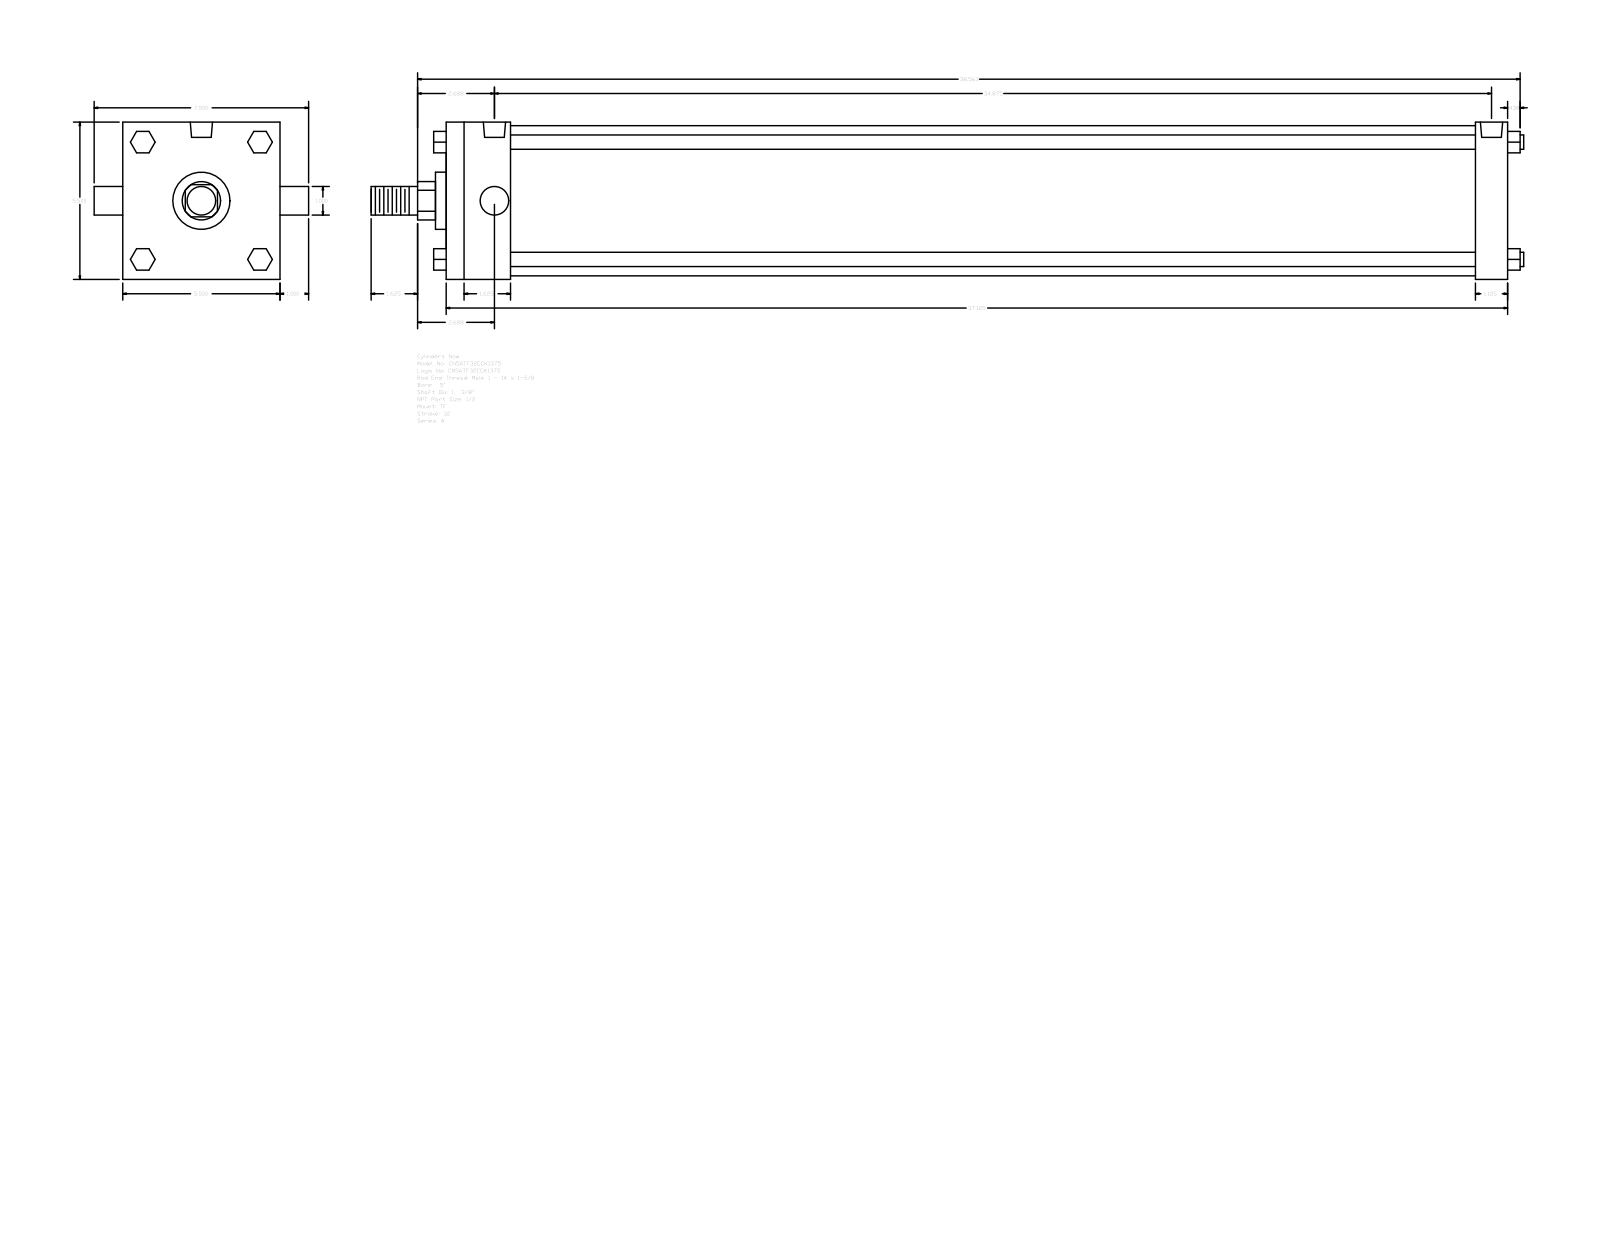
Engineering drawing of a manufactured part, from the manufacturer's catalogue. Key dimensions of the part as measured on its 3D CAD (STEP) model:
Part name (STEP PRODUCT): A_TF__0500_1.375
STEP written by: GSSL Pune (CONFIG_CONTROL_DESIGN)
Units: millimetres
Bodies: 0 solids, 120 faces (92 planar, 28 cylindrical, 0 other)
Overall size (bounding box): 1023.94 × 190.5 × 139.7
Round holes (diameter × count): ⌀8.73 ×3, ⌀19.77 ×2
Round bosses / shafts (diameter × count): ⌀12.7 ×4, ⌀25.4 ×2, ⌀133.35 ×1, ⌀50.8 ×1, ⌀34.92 ×1
Partial cylindrical surfaces — rounded edges, fillets, slot ends (radius × count): R17.06 ×1
Main face-to-face distances: 139.7, 942.98, 57.15, 28.58, 914.4, 857.25, 885.83, 19.05, 52.07, 90.18
Hole centre spacings: 2.39, 883.44, 881.05, 885.83
